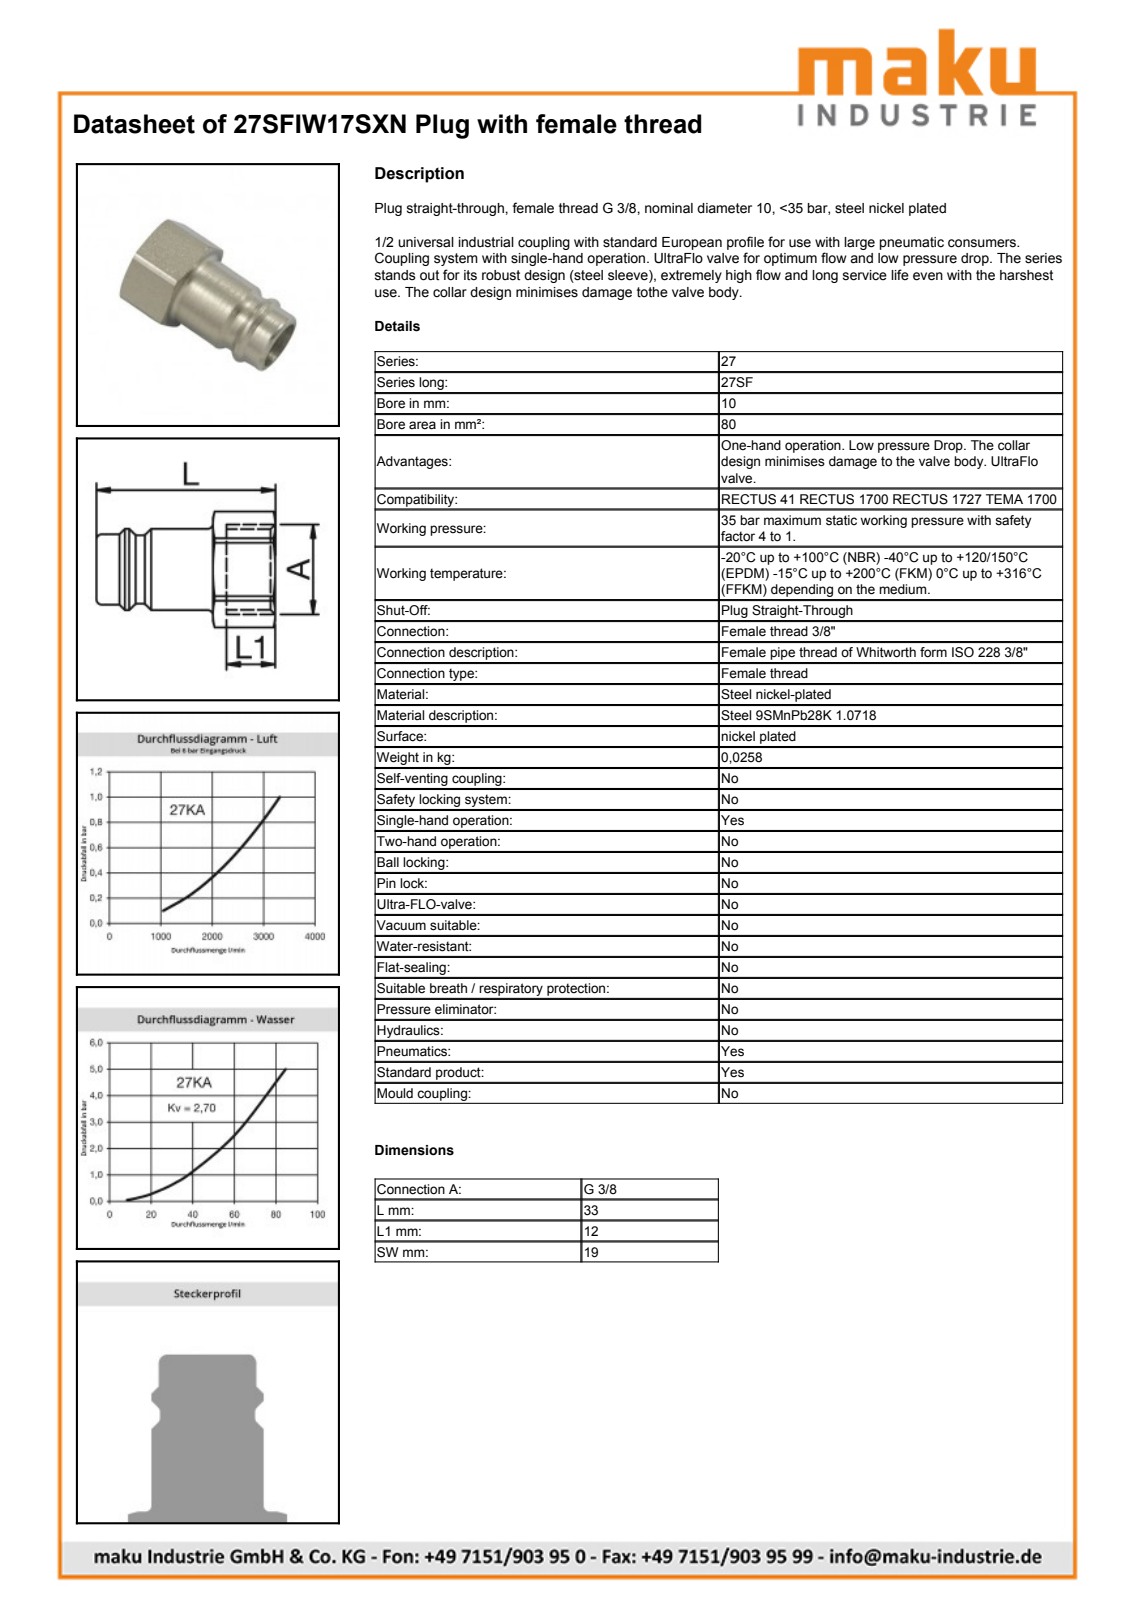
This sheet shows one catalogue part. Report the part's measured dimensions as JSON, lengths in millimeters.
{"part_name": "D106718", "step_written_by": "Autodesk Inventor 2011 (AUTOMOTIVE_DESIGN)", "units": "millimeters", "bodies": {"solids": 1, "faces": 42, "planar": 10, "cylindrical": 12, "other": 20}, "overall_size": [33, 21.4, 19], "volume_mm3": 3543, "surface_area_mm2": 3290, "round_holes": [[10, 1], [14.95, 1]], "round_bosses_or_shafts": [[15, 1], [13, 1], [12.65, 1]], "partial_cylinders_radius": [[10.7, 1]], "face_to_face_distances": [19, 9, 2.5, 11.5, 21.5, 24, 33]}
